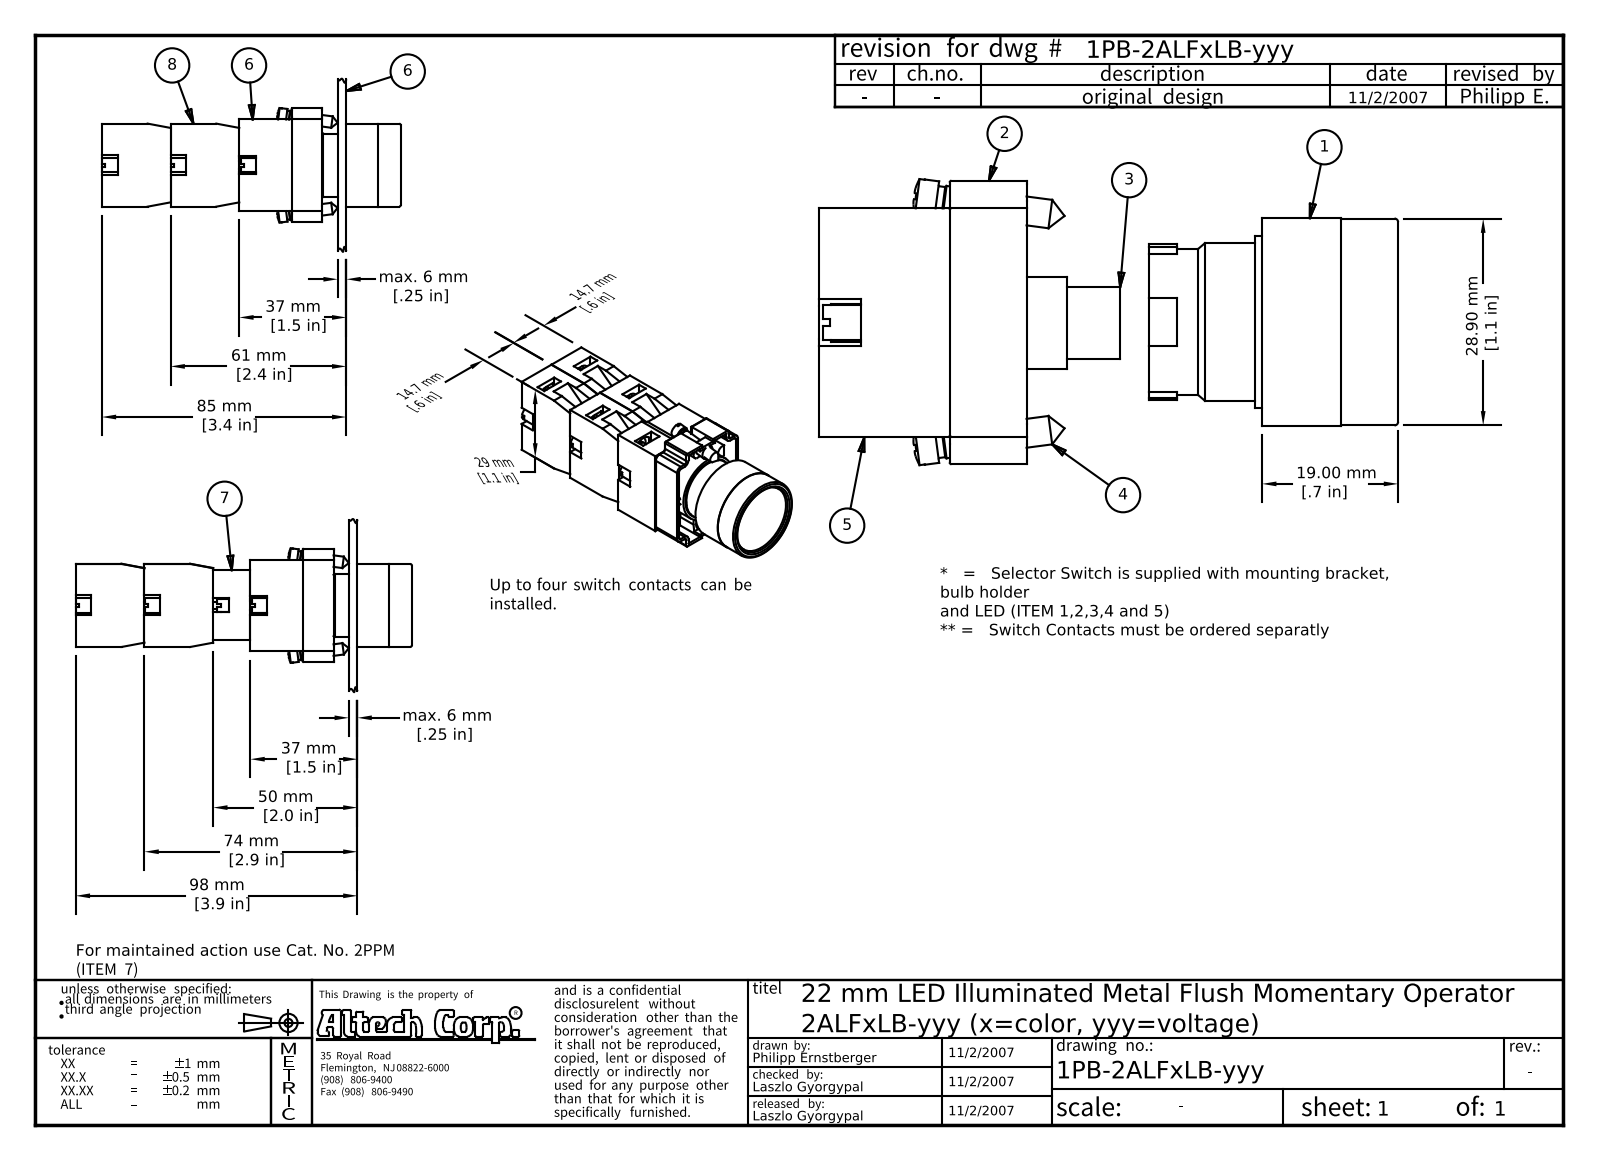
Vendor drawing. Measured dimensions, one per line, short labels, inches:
name: 2ALFxLB-yyy_assembly; 2BRK; DIN 7985 (Z) M4x18-Z; S1 (+8 more)
written by: Autodesk Inventor 2008 (AUTOMOTIVE_DESIGN)
unit: in
bodies: 28 solids, 1086 faces (588 planar, 180 cylindrical, 318 other)
size: 4.11 × 2.38 × 1.772
volume: 4.45 in³; area: 74.24 in²
holes: 5× ⌀0.098, 2× ⌀0.102, 1× ⌀0.524, 1× ⌀0.709, 1× ⌀0.866, 1× ⌀0.876, 1× ⌀0.886, 1× ⌀0.984, 1× ⌀1.063
bosses: 8× ⌀0.118, 6× ⌀0.108, 4× ⌀0.197, 4× ⌀0.059, 2× ⌀0.157, 2× ⌀0.144, 1× ⌀1.142, 1× ⌀1.138
rounds: 14× R0.039, 10× R0.01, 8× R0.028, 5× R0.089, 4× R0.02, 4× R0.031, 4× R0.071, 4× R0.079
face distances: 0.583, 0.579, 0.118, 0.945, 0.589, 0.593, 1.171, 0.752, 1.161, 0.634
hole spacings: 0.572, 0.257, 0.259, 0.512, 1.019, 1.024, 1.034, 1.144
